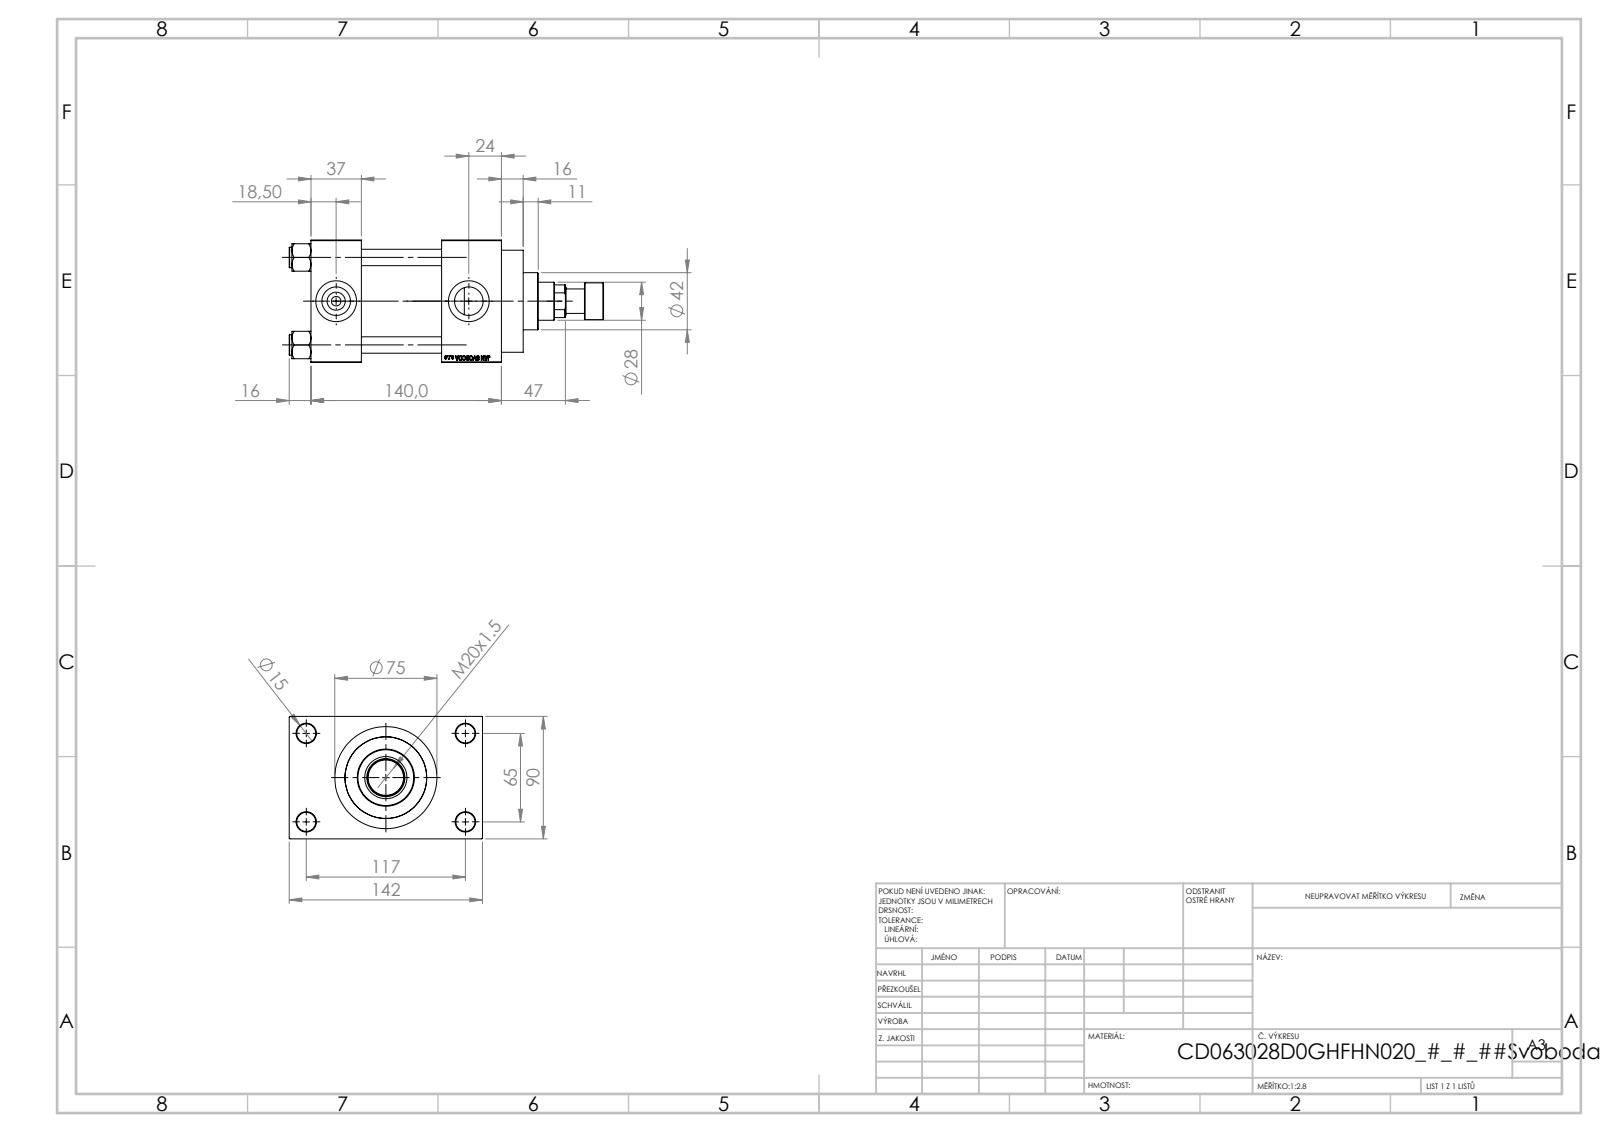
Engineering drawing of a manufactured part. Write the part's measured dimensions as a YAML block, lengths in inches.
part_name: "V215CD_NUT_M5_D; V215CD_VC_A; V215CR_ROD_END_F; V215CD_D_Body (+2 more)"
step_written_by: "SolidWorks 2019 (CONFIG_CONTROL_DESIGN)"
units: inches
bodies: {solids: 12, faces: 1117, planar: 501, cylindrical: 92, other: 524}
overall_size: [9.094, 5.591, 3.543]
volume: 67.61
surface_area: 315.5
round_holes:
  - {diameter: 0.472, count: 4}
  - {diameter: 0.551, count: 4}
  - {diameter: 0.276, count: 2}
  - {diameter: 0.825, count: 2}
  - {diameter: 1.181, count: 2}
  - {diameter: 0.728, count: 1}
  - {diameter: 1.102, count: 1}
  - {diameter: 1.22, count: 1}
  - {diameter: 1.969, count: 1}
  - {diameter: 2.362, count: 1}
  - {diameter: 2.48, count: 1}
round_bosses_or_shafts:
  - {diameter: 0.591, count: 4}
  - {diameter: 2.953, count: 1}
  - {diameter: 2.717, count: 1}
  - {diameter: 1.654, count: 1}
  - {diameter: 1.063, count: 1}
  - {diameter: 0.709, count: 1}
face_to_face_distances: [3.543, 2.323, 1.457, 3.78, 5.512, 4.055, 1.732, 1.024, 4.567, 4.685]
hole_center_spacings: [1.037, 1.79, 2.531, 2.635, 2.748, 3.569, 4.383, 2.559]
